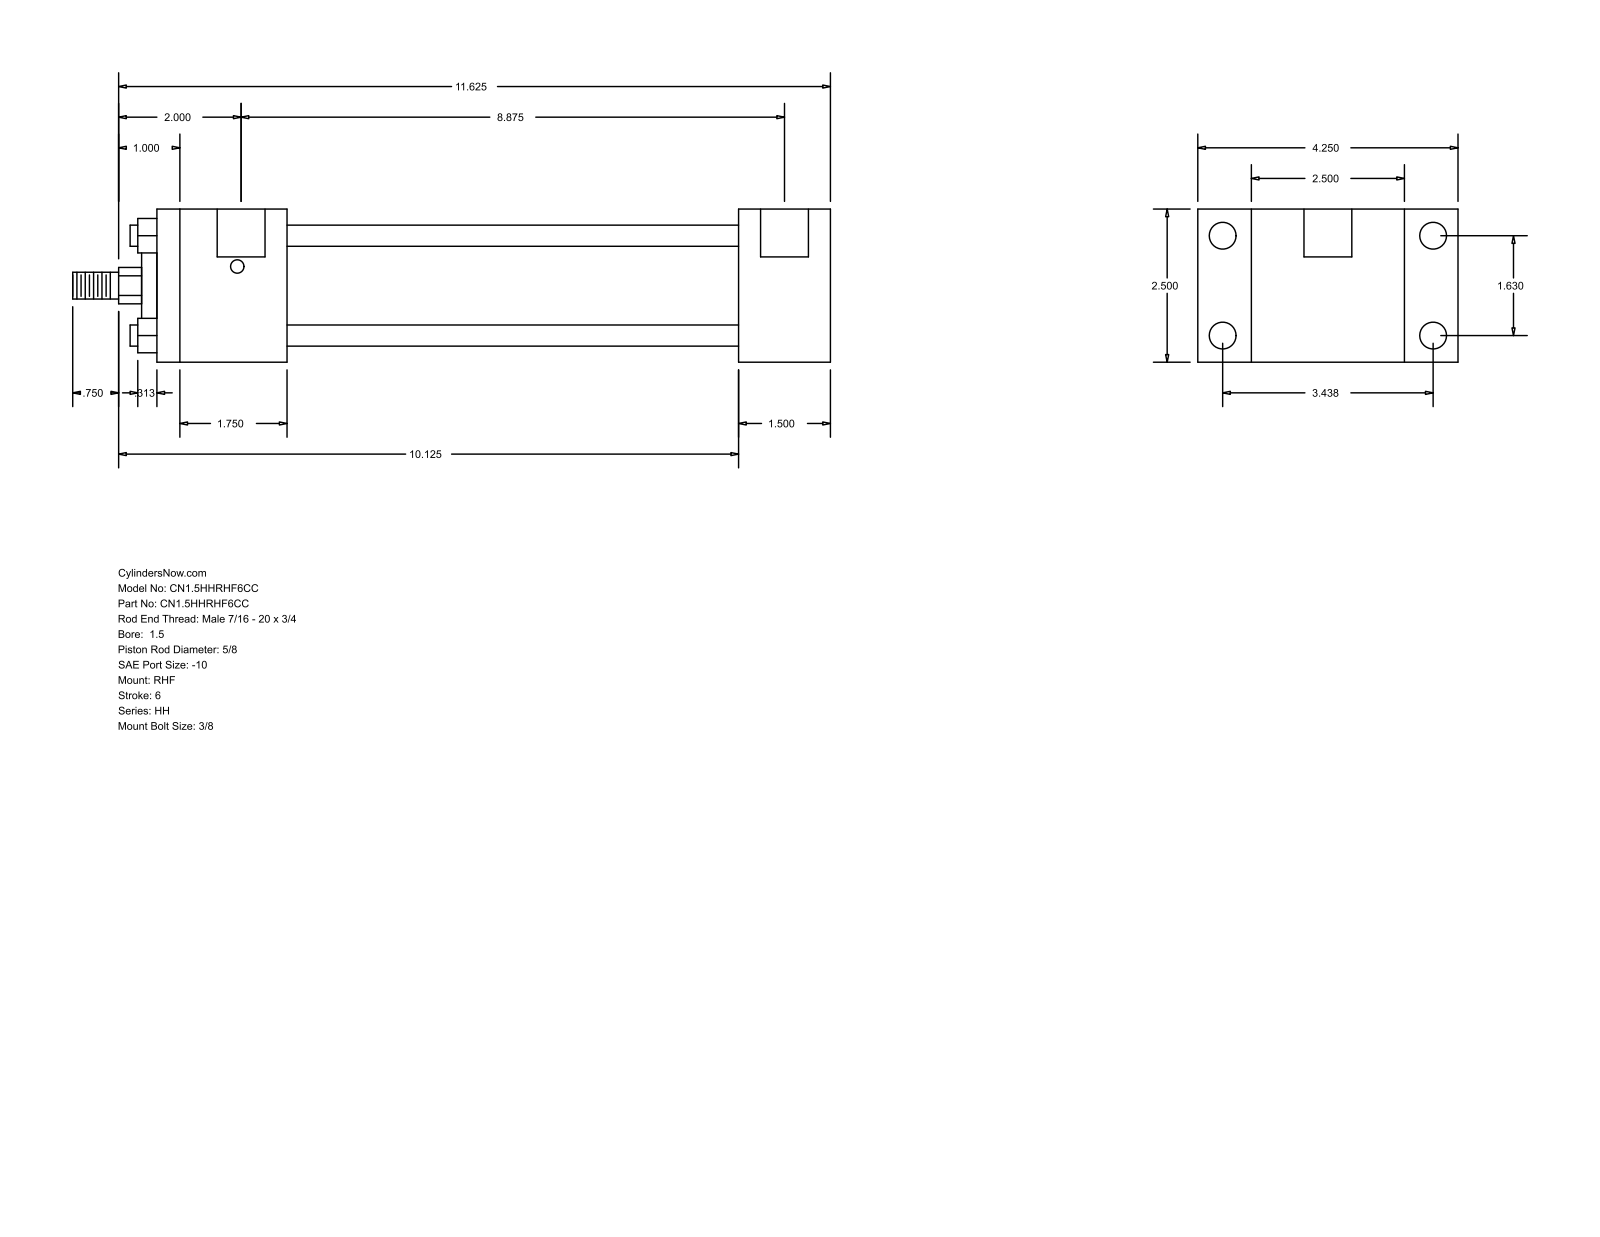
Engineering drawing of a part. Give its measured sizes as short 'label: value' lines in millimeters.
name: HH_RHF__0150_0.625
written by: GSSL Pune (CONFIG_CONTROL_DESIGN)
unit: mm
bodies: 0 solids, 88 faces (60 planar, 28 cylindrical, 0 other)
size: 314.32 × 107.95 × 63.5
holes: 4× ⌀5.56, 4× ⌀11.13, 2× ⌀19.84
bosses: 4× ⌀8.76, 1× ⌀44.45, 1× ⌀28.57, 1× ⌀15.88, 1× ⌀11.11
rounds: 1× R7.54
face distances: 63.5, 22.23, 85.73, 38.09, 241.3, 279.39, 107.96, 53.97, 187.33, 225.42
hole spacings: 41.4, 87.32, 96.64, 228.6, 1.58, 1.59, 225.43, 227.01
